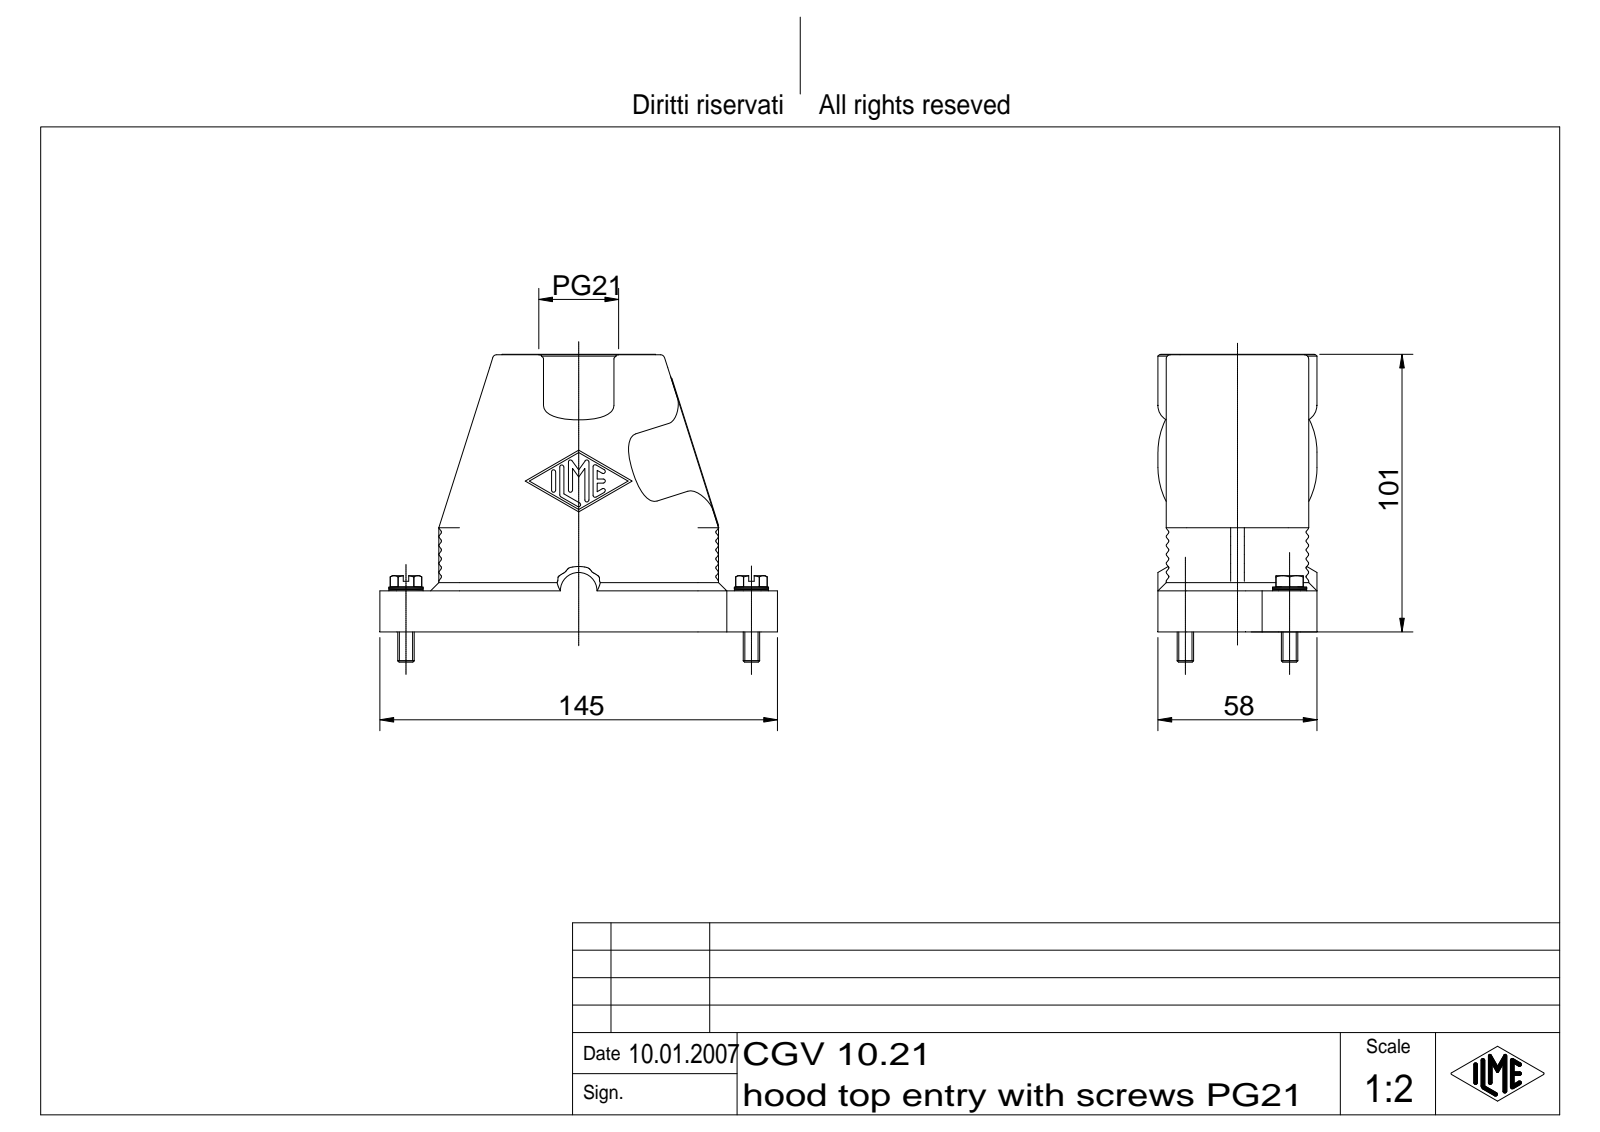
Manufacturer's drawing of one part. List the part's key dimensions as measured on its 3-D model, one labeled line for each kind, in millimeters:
Part name (STEP PRODUCT): CGV 10.21
STEP written by: Autodesk Inventor 7 (AUTOMOTIVE_DESIGN)
Units: millimetres
Bodies: 3 solids, 781 faces (194 planar, 203 cylindrical, 384 other)
Overall size (bounding box): 145 × 112.2 × 58
Volume: 206 978 mm³ · Surface area: 72 784 mm²
Round holes (diameter × count): ⌀2.46 ×2, ⌀3.2 ×2, ⌀6.6 ×2, ⌀15 ×2, ⌀26.78 ×1
Round bosses / shafts (diameter × count): ⌀56 ×2, ⌀12.5 ×2, ⌀6 ×2, ⌀58 ×1
Partial cylindrical surfaces — rounded edges, fillets, slot ends (radius × count): R0.5 ×39, R0.75 ×14, R7.5 ×8, R6 ×6, R1.5 ×4, R3 ×4, R5.75 ×2, R10.5 ×2
Main face-to-face distances: 3, 52, 49, 6, 55, 2.5, 46, 0.5, 58, 3.5
Hole centre spacings: 34.94, 97.1, 63.07, 131.61
